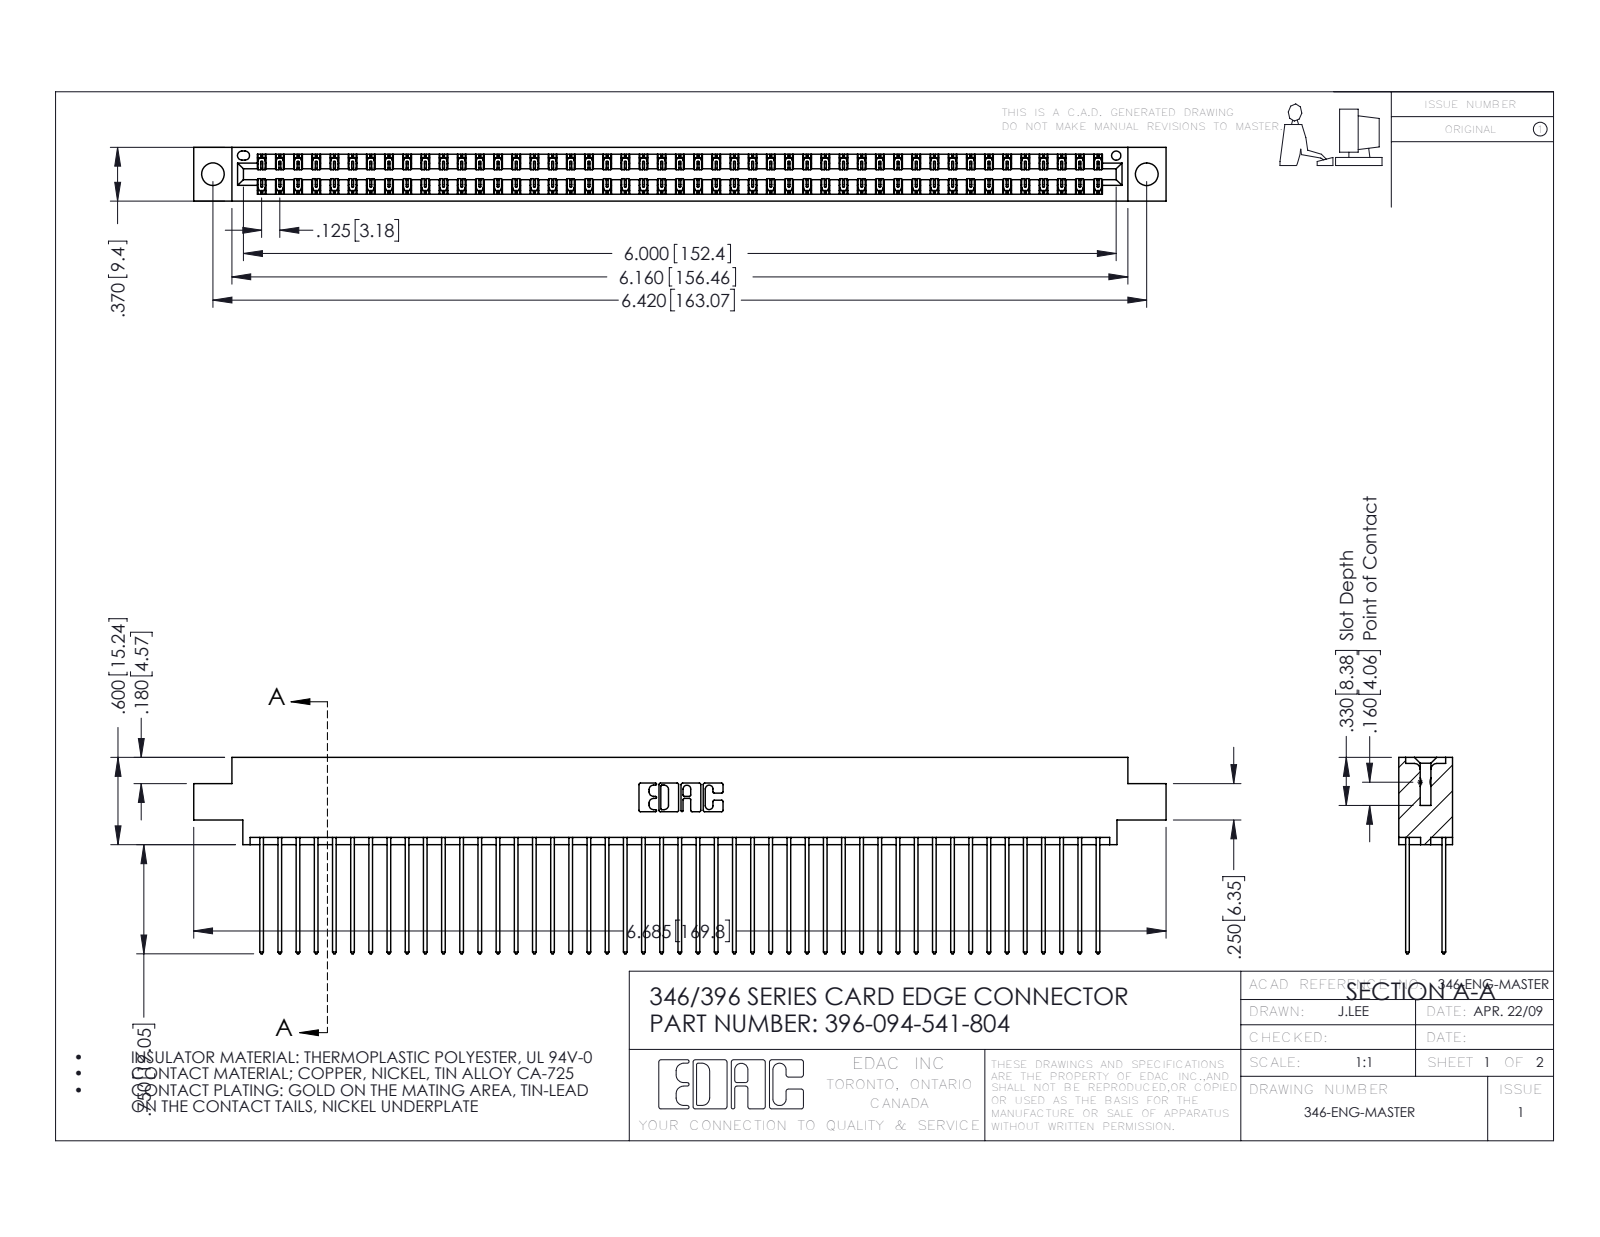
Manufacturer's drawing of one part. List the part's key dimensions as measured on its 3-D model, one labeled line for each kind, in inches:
Part name (STEP PRODUCT): 345-292-001_345-293-141; 396-094-541-804; 346 Part_0.170 Offset - 0.156 Dia-TH
STEP written by: SolidWorks 2016 (CONFIG_CONTROL_DESIGN)
Units: inches
Bodies: 95 solids, 5014 faces (3370 planar, 1644 cylindrical, 0 other)
Overall size (bounding box): 6.685 × 1.35 × 0.37
Volume: 1.031 in³ · Surface area: 40.11 in²
Round holes (diameter × count): ⌀0.156 ×2, ⌀0.064 ×1
Partial cylindrical surfaces — rounded edges, fillets, slot ends (radius × count): R0.006 ×141, R0.01 ×94, R0.01 ×22, R0.007 ×6, R0.031 ×6, R0.026 ×3, R0.014 ×2, R0.022 ×2
Main face-to-face distances: 0.048, 0.322, 0.25, 0.072, 0.298, 0.025, 0.37, 0.275, 0.225, 0.148
Hole centre spacings: 0.246, 6.211, 6.42
